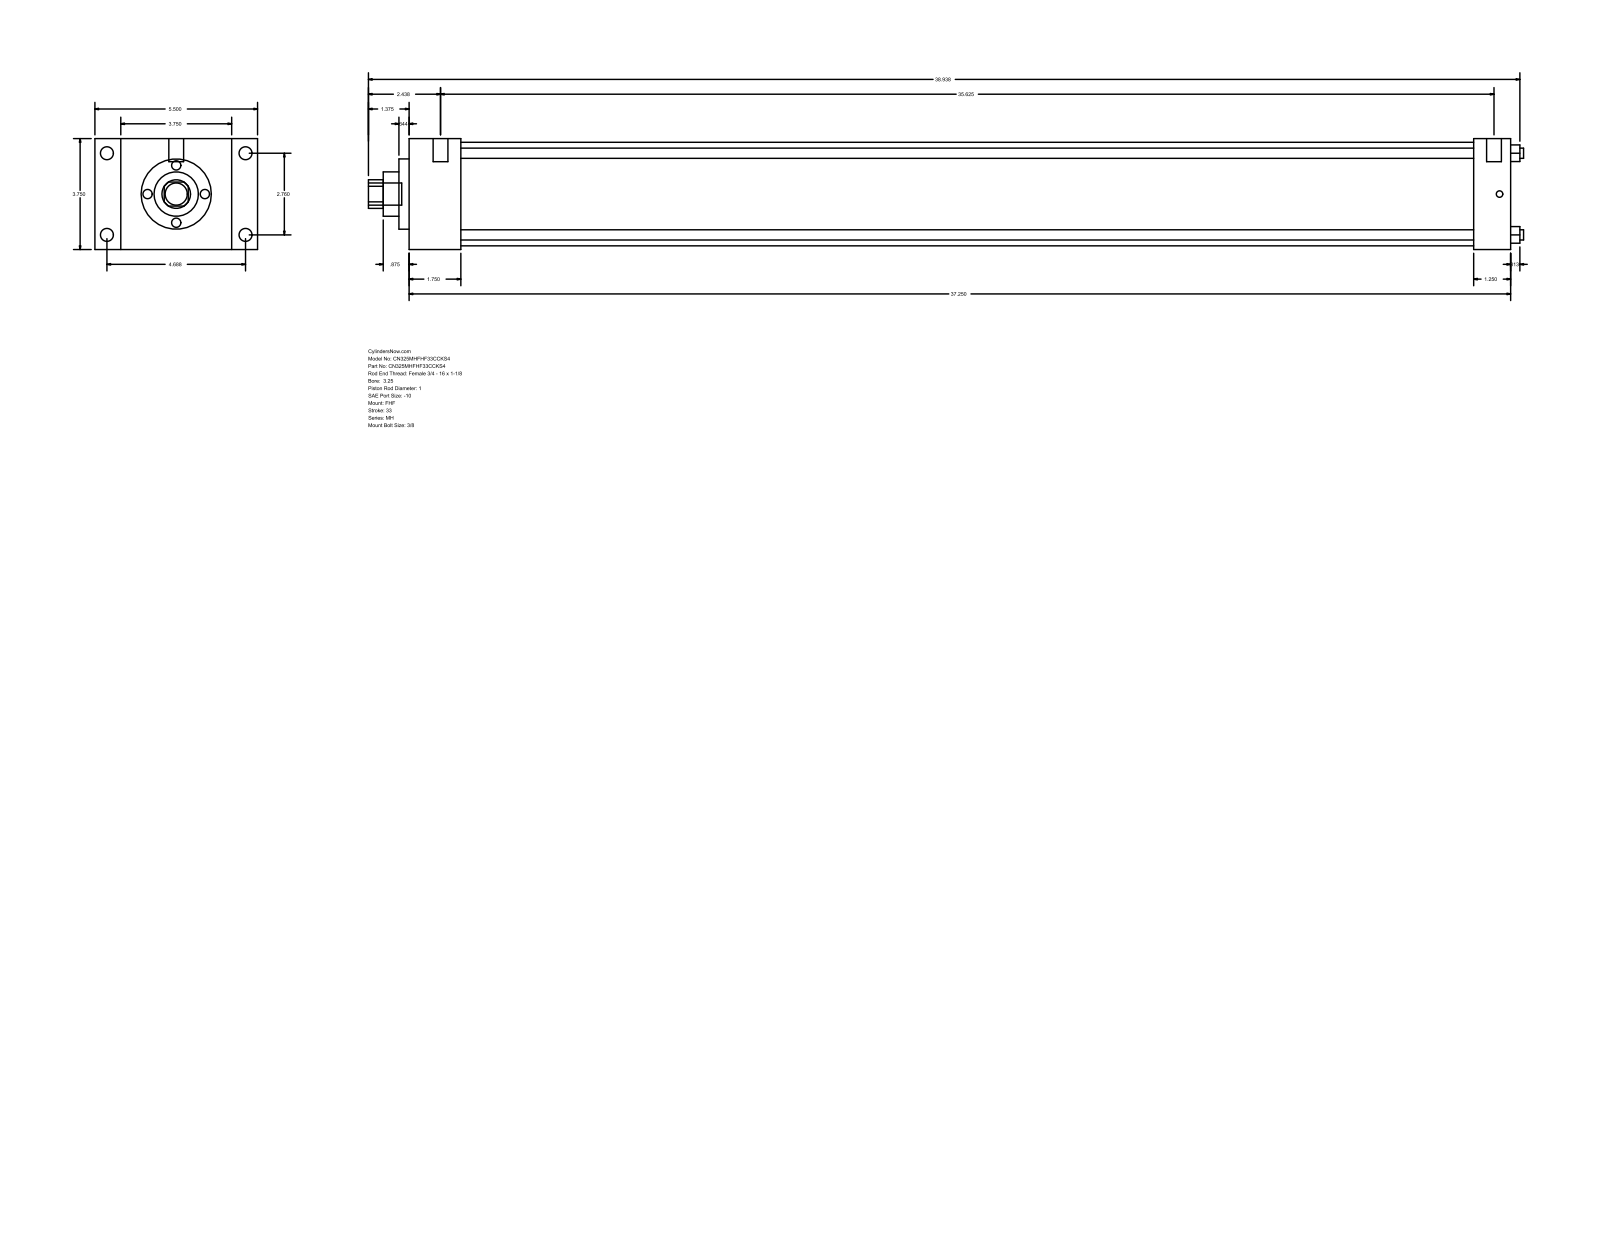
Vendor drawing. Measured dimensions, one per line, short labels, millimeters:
name: MH_FHF__0325_1
written by: GSSL Pune (CONFIG_CONTROL_DESIGN)
unit: mm
bodies: 0 solids, 90 faces (61 planar, 29 cylindrical, 0 other)
size: 992.19 × 139.7 × 95.25
holes: 4× ⌀8.76, 1× ⌀25.4, 1× ⌀38.1, 1× ⌀60.33, 1× ⌀88.9
bosses: 4× ⌀11.13, 4× ⌀5.56, 2× ⌀12.7, 1× ⌀19.05
rounds: 1× R12.29
face distances: 95.24, 946.16, 44.46, 901.7, 22.23, 117.47, 139.7, 914.41, 869.95, 31.75
hole spacings: 49.57, 70.1, 99.14
